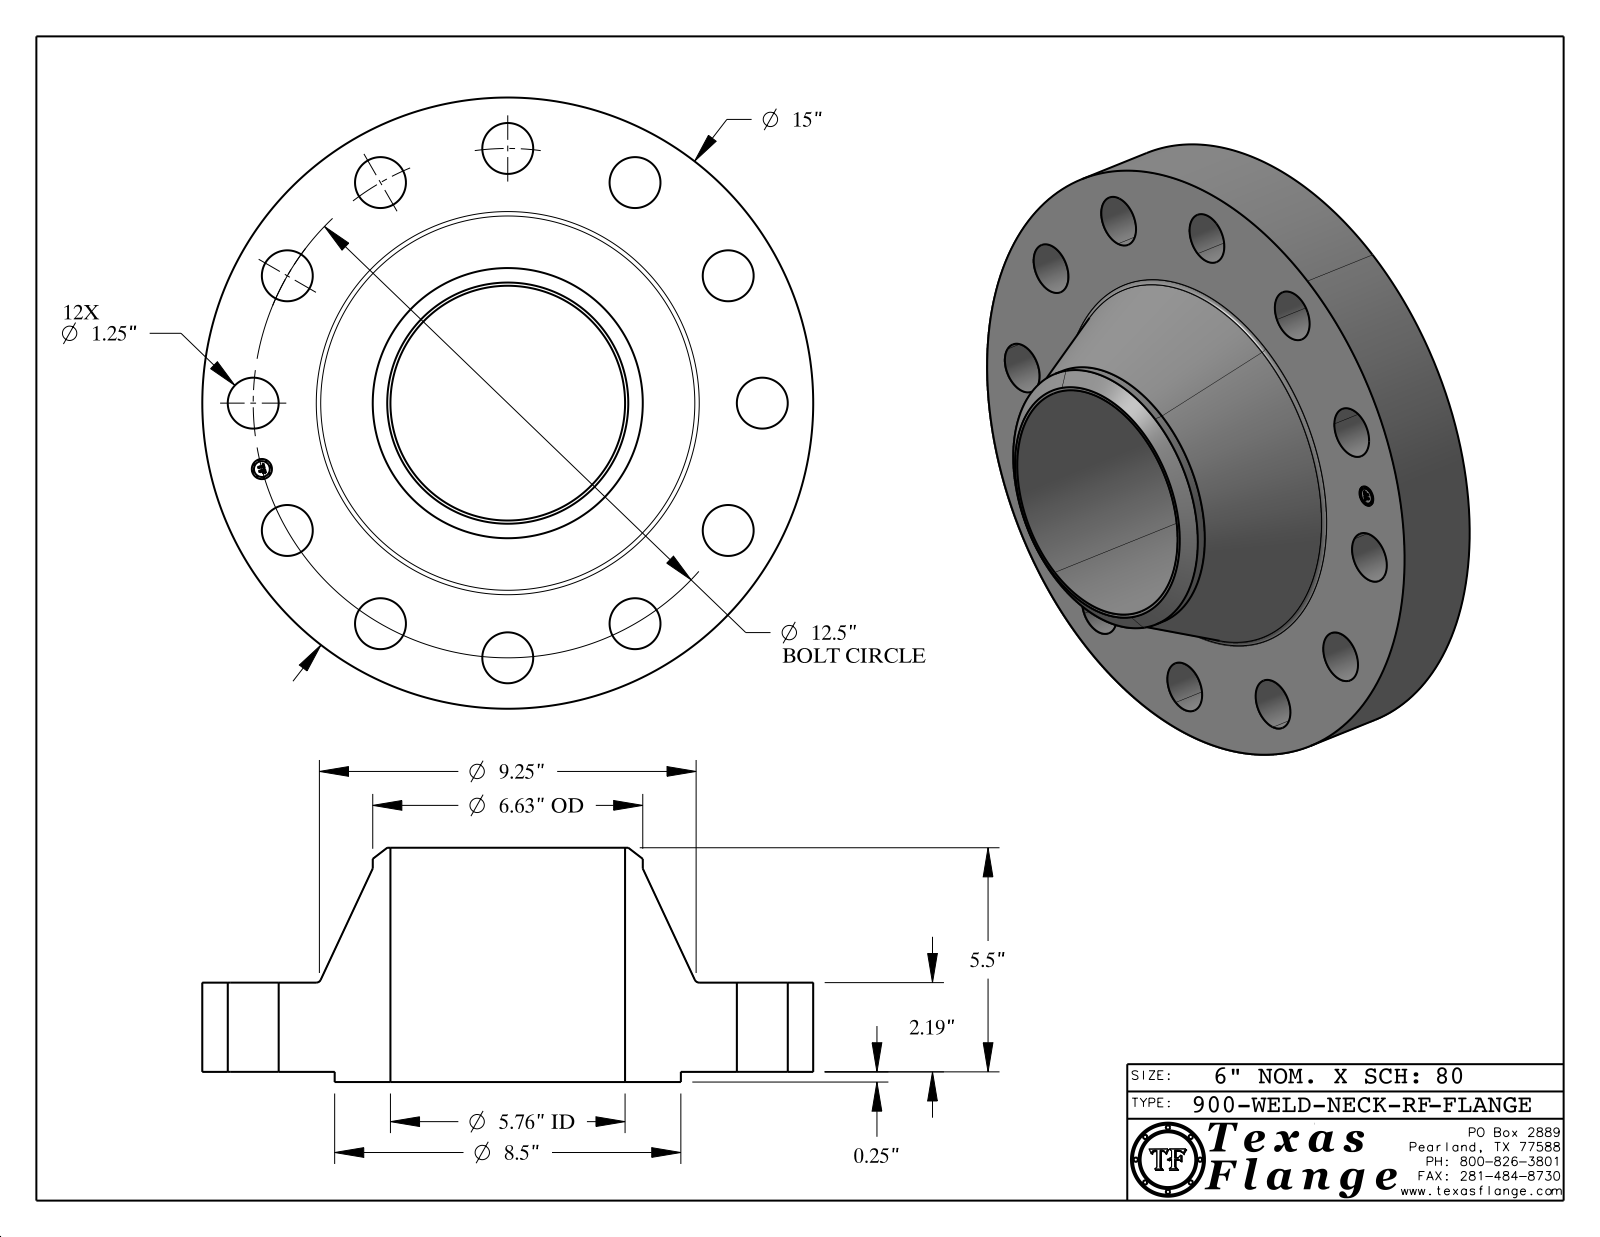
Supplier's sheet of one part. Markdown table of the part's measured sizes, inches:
| quantity | value |
| --- | --- |
| part name | 900-WELD-NECK-RF |
| STEP written by | CATIA V5 STEP AP214 (AUTOMOTIVE_DESIGN) |
| units | inches |
| bodies | 1 solid, 427 faces (369 planar, 52 cylindrical, 6 other) |
| overall size | 15 × 15 × 5.75 |
| volume | 375.6 in³ |
| surface area | 639.8 in² |
| round holes (diameter × count) | 1.25 × 12, 0.495 × 1, 5.761 × 1 |
| round bosses / shafts (diameter × count) | 0.03 × 8, 15 × 1, 8.5 × 1, 6.63 × 1, 0.39 × 1 |
| main face-to-face distances | 2.19, 0.25, 2.44, 5.75, 5.5, 3.31, 2.425, 2.175, 0.015, 3.325 |
| hole center spacings | 6.25, 8.839, 3.235, 10.826, 12.074, 12.5, 3.235, 6.25 |
